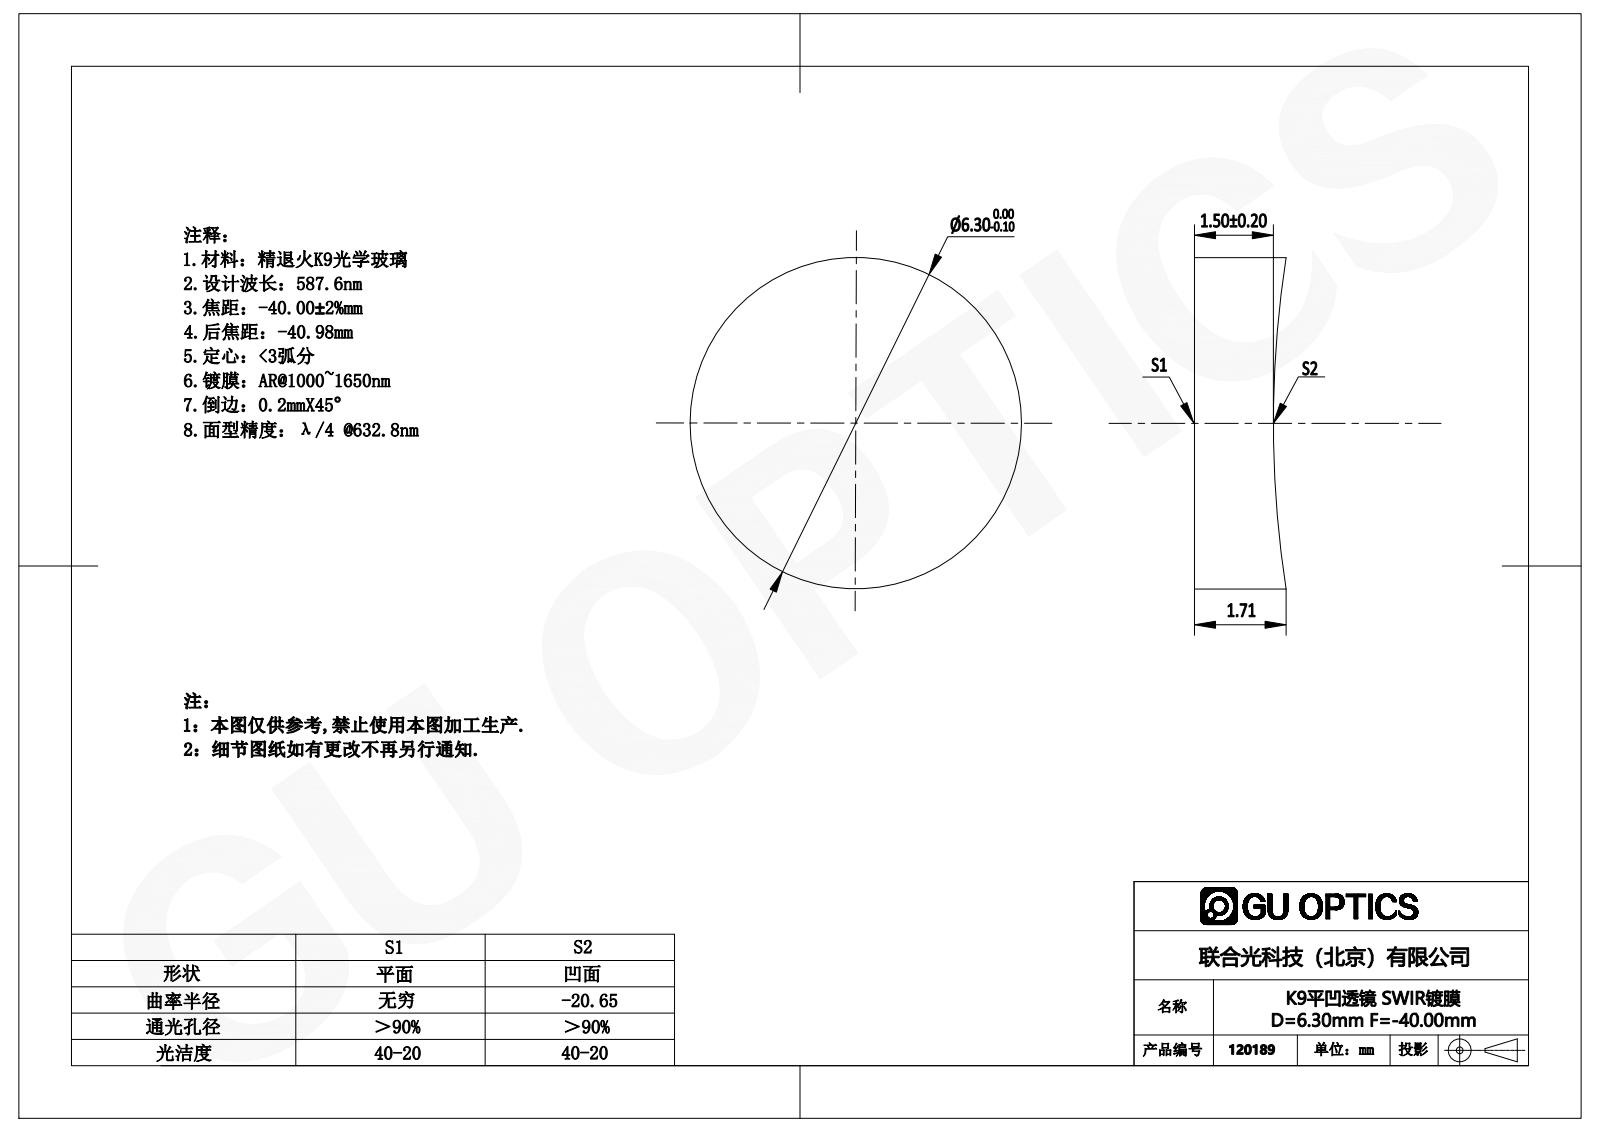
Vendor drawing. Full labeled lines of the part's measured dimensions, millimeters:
Part name (STEP PRODUCT): 120129
STEP written by: SolidWorks 2016 (AUTOMOTIVE_DESIGN)
Units: millimetres
Bodies: 1 solid, 5 faces (1 planar, 2 cylindrical, 2 other)
Overall size (bounding box): 6.3 × 6.3 × 1.74
Volume: 51 mm³ · Surface area: 97 mm²
Round bosses / shafts (diameter × count): ⌀6.3 ×1
